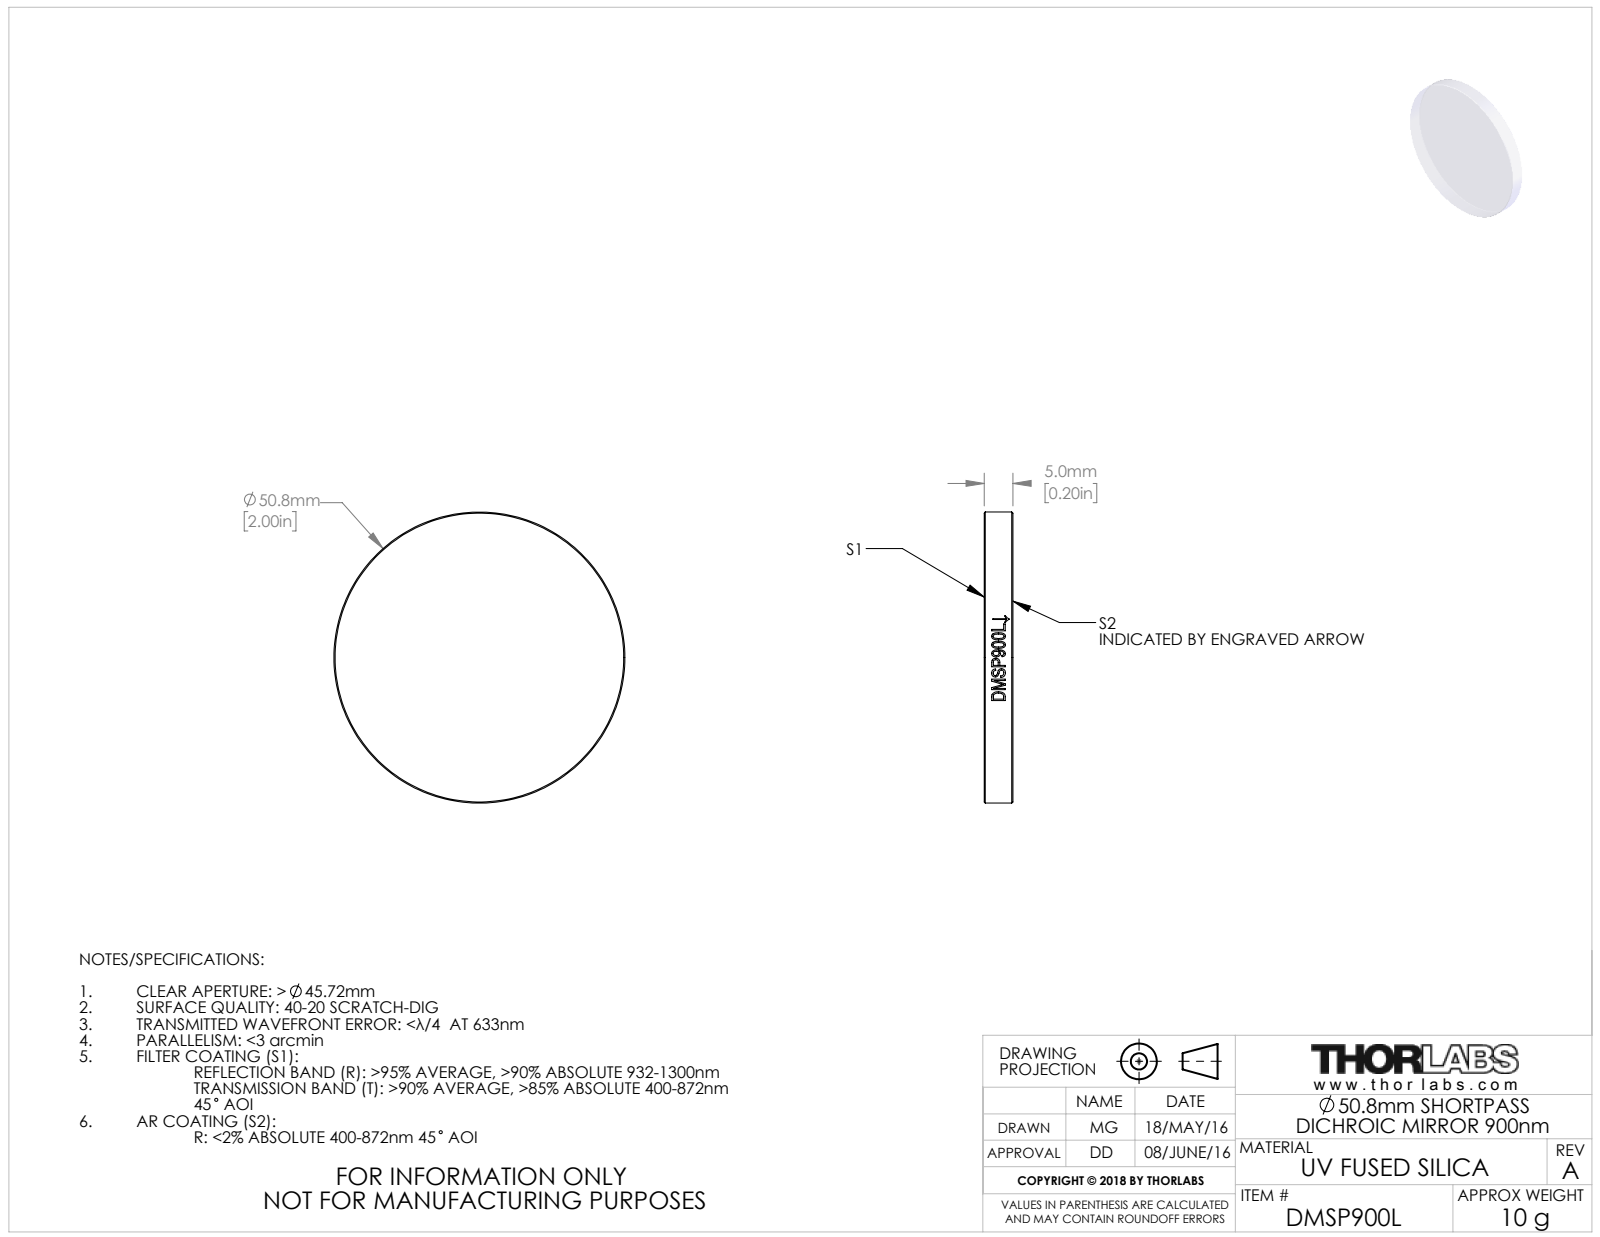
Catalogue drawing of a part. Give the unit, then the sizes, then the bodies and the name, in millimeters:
Units: millimetres
Overall size (bounding box): 50.8 × 50.8 × 5
Round bosses / shafts (diameter × count): ⌀50.8 ×1
Main face-to-face distances: 5
Volume: 10 131 mm³ · Surface area: 4 814 mm²
Bodies: 1 solid, 22 faces (2 planar, 16 cylindrical, 4 other)
Part name (STEP PRODUCT): TTN045171-E0W
STEP written by: SolidWorks 2016 (CONFIG_CONTROL_DESIGN)
